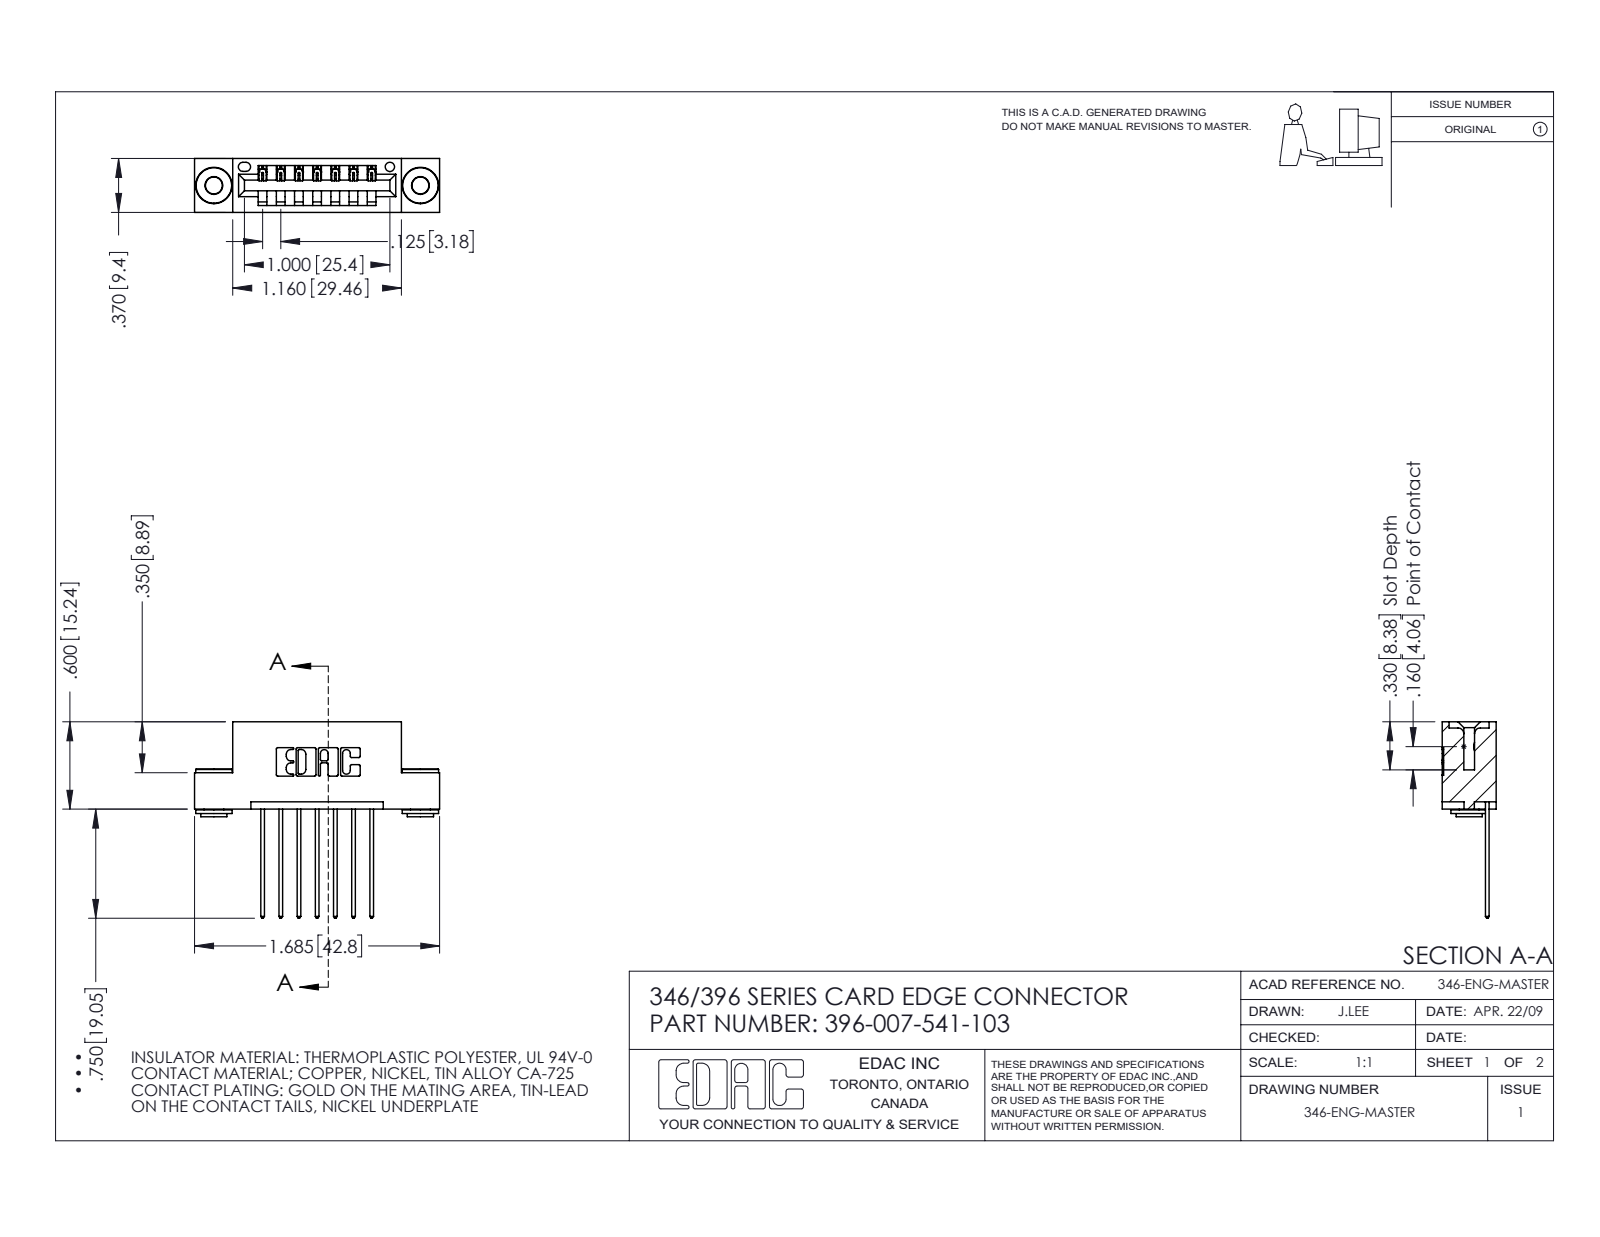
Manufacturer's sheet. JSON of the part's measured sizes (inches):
{"part_name": "345-292-001_345-293-141; 345-250-002_345-250-002-102; 396-007-541-103; 346 Part_Flush Mounting Lugs - 0.156 Dia-TH", "step_written_by": "SolidWorks 2016 (CONFIG_CONTROL_DESIGN)", "units": "inches", "bodies": {"solids": 10, "faces": 566, "planar": 366, "cylindrical": 192, "other": 8}, "overall_size": [1.685, 1.35, 0.37], "volume_in3": 0.238, "surface_area_in2": 7.52, "round_holes": [[0.116, 2], [0.156, 2], [0.064, 1]], "round_bosses_or_shafts": [[0.25, 2], [0.18, 2], [0.136, 2]], "partial_cylinders_radius": [[0.01, 22], [0.006, 14], [0.01, 14], [0.007, 6], [0.031, 6], [0.026, 3], [0.031, 2], [0.04, 2]], "face_to_face_distances": [0.25, 0.048, 0.322, 0.37, 0.025, 0.072, 0.298, 0.148, 0.222, 0.1], "hole_center_spacings": [0.246, 1.217, 1.42]}
